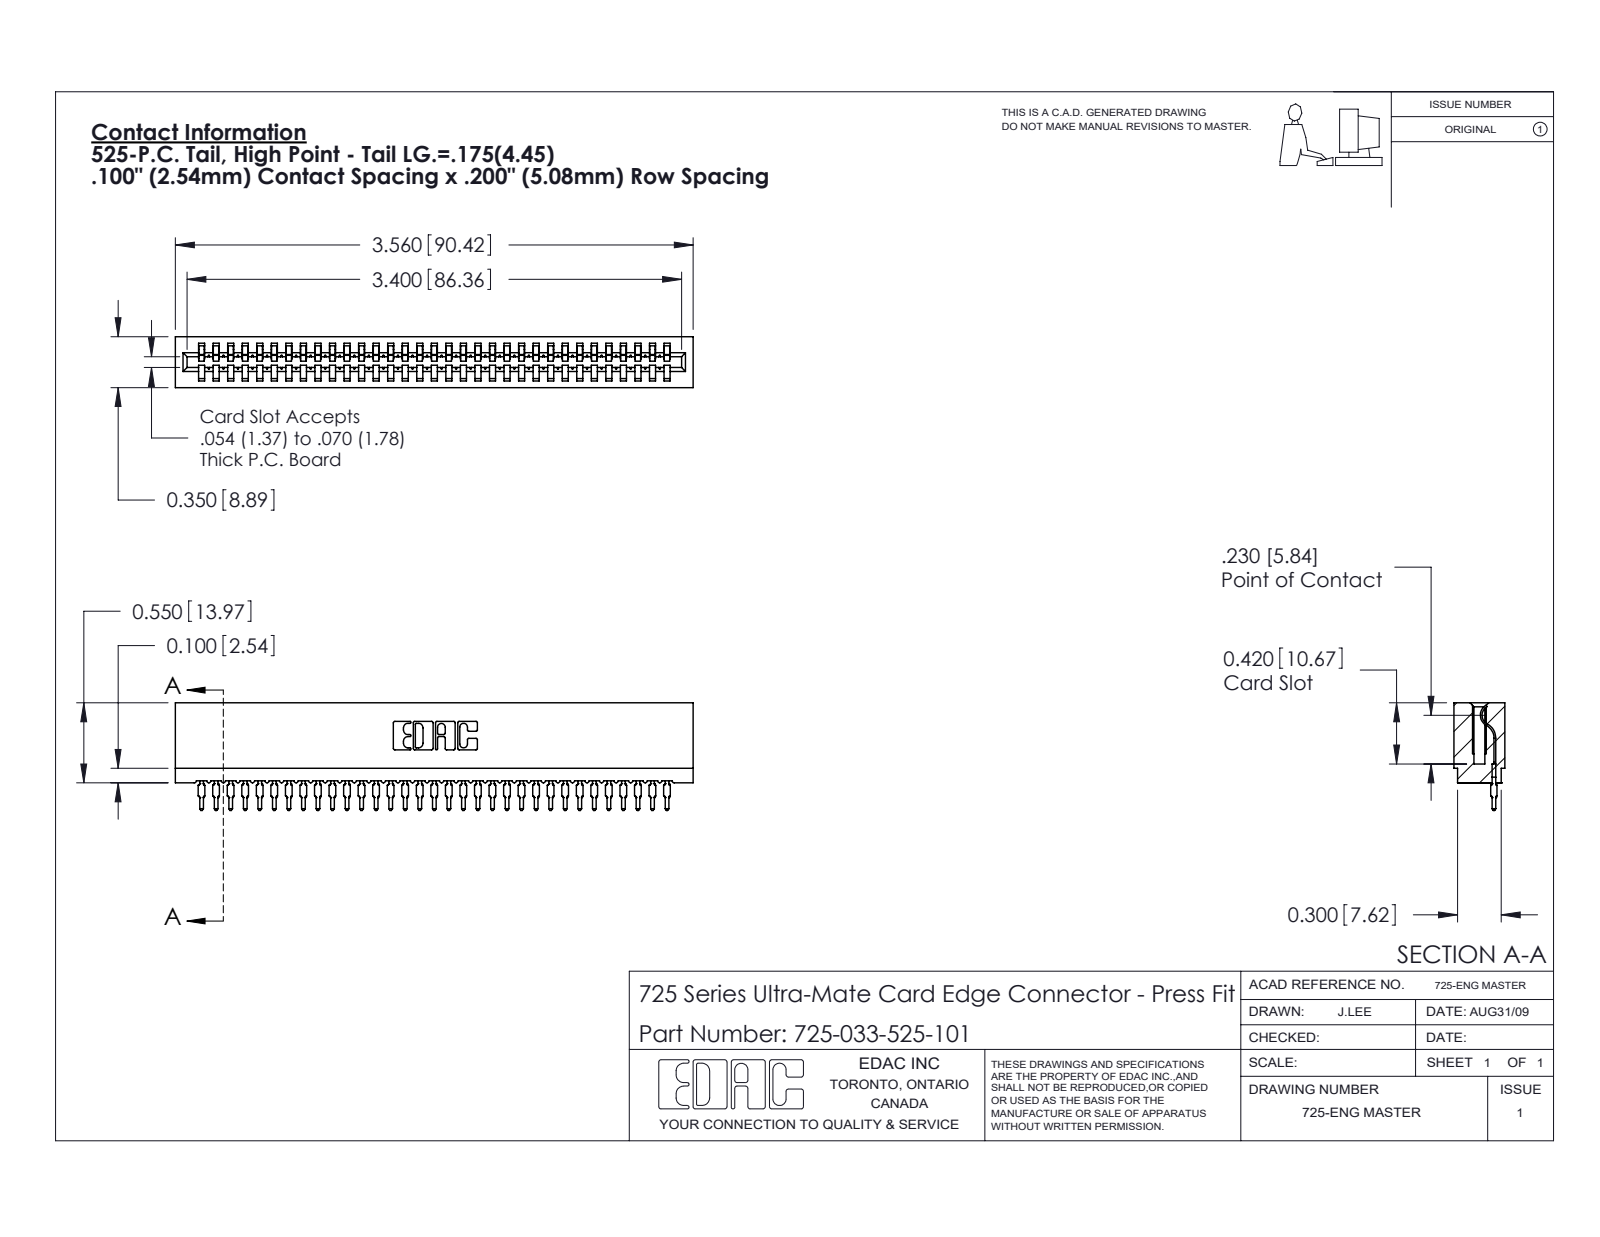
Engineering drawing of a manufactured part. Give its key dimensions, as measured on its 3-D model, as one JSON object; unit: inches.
{"part_name": "725 Part_Insulator Option - 01; 745-292-001_525; 725-033-525-101", "step_written_by": "SolidWorks 2020 (CONFIG_CONTROL_DESIGN)", "units": "inches", "bodies": {"solids": 34, "faces": 3791, "planar": 2266, "cylindrical": 667, "other": 858}, "overall_size": [3.56, 0.741, 0.35], "volume_in3": 0.42, "surface_area_in2": 20.19, "partial_cylinders_radius": [[0.015, 66], [0.021, 66], [0.01, 22], [0.007, 6], [0.031, 6], [0.005, 4], [0.011, 4], [0.026, 3]], "face_to_face_distances": [0.2, 0.1, 0.35, 0.3, 0.212, 0.138, 0.4, 0.5, 0.045, 0.305]}
